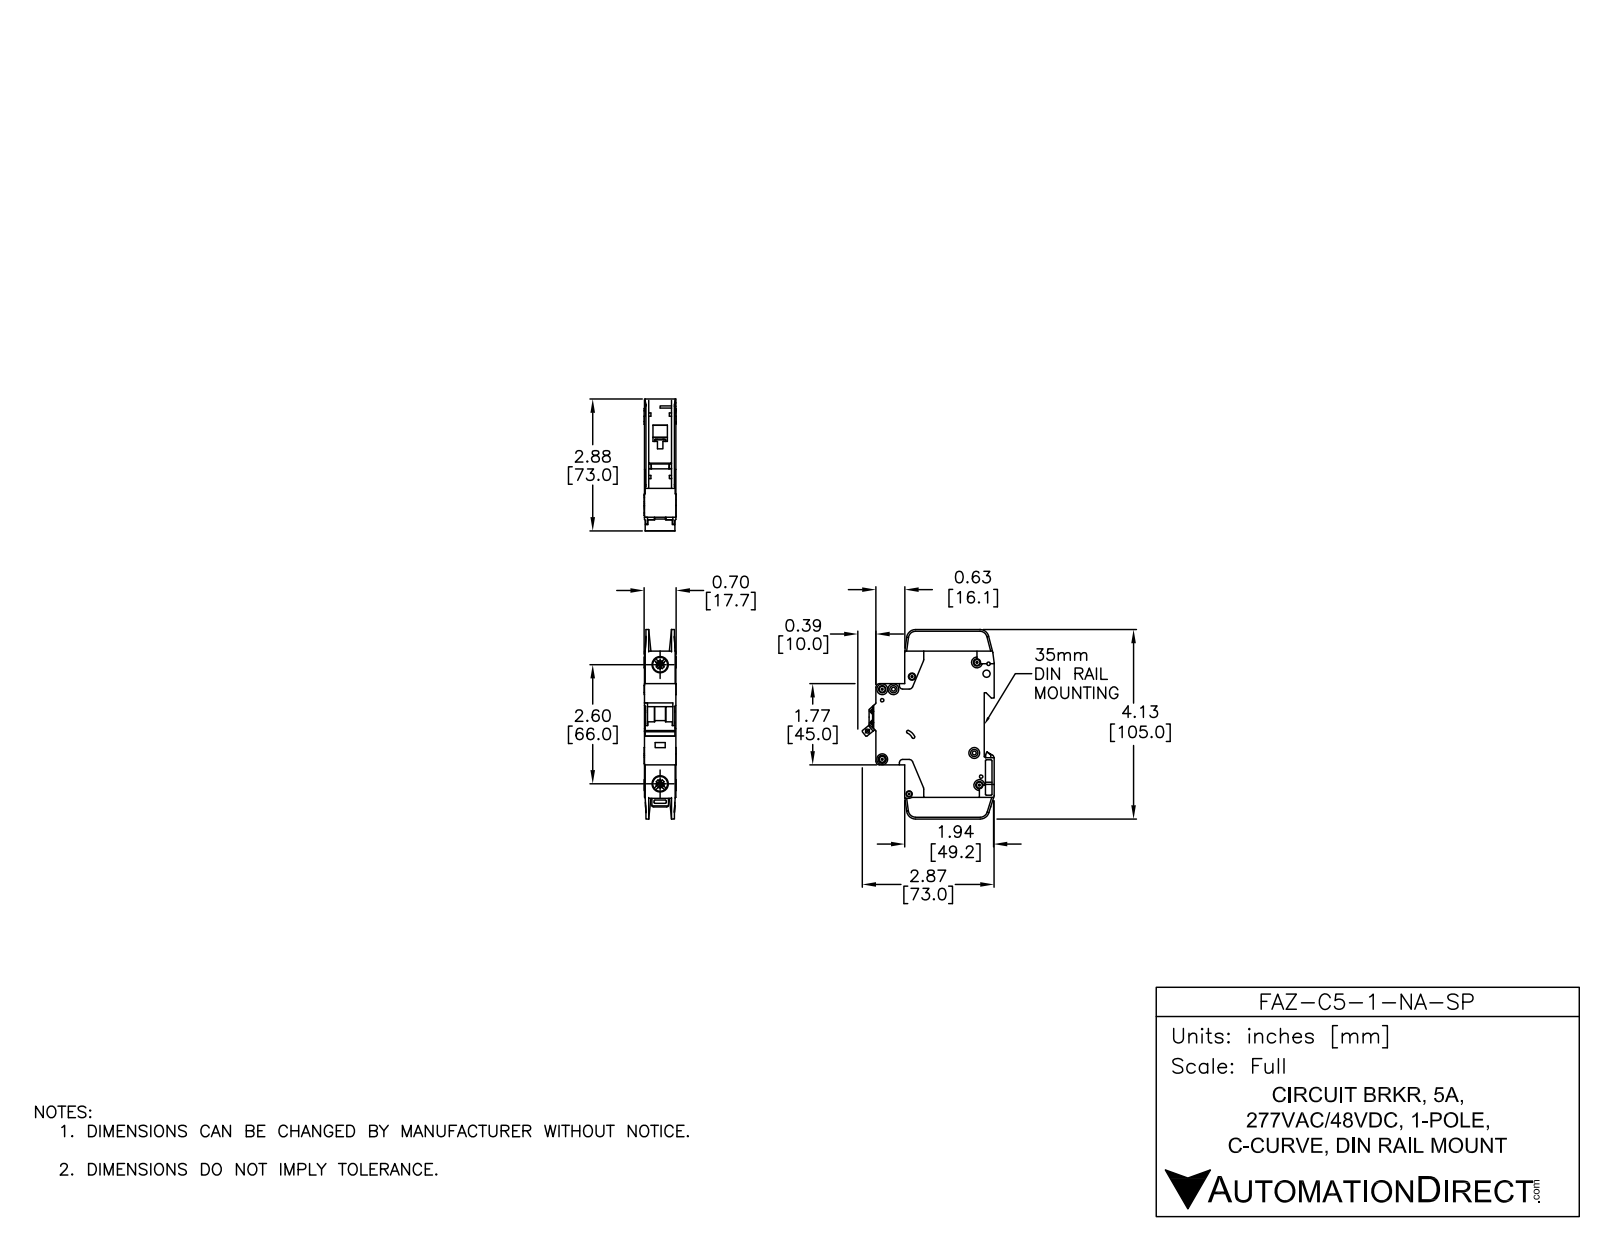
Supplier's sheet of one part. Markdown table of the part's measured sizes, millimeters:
| quantity | value |
| --- | --- |
| part name | FAZ-C50-1-NA-SP |
| STEP written by | SolidWorks 2014 (AUTOMOTIVE_DESIGN) |
| units | millimeters |
| bodies | 3 solids, 784 faces (409 planar, 263 cylindrical, 112 other) |
| overall size | 105 × 73.04 × 17.7 |
| volume | 77 695 mm³ |
| surface area | 24 740 mm² |
| round holes (diameter × count) | 3.6 × 7, 1.09 × 2, 1.5 × 2, 4 × 2, 7.15 × 2, 8.2 × 2, 1.9 × 1, 2.15 × 1, 2.2 × 1, 2.55 × 1, 3.3 × 1, 3.4 × 1 |
| round bosses / shafts (diameter × count) | 6 × 7, 2.5 × 1 |
| partial cylindrical surfaces (radius × count) | 0.25 × 29, 0.5 × 18, 1 × 10, 2 × 10, 5 × 5, 4 × 4, 1.8 × 3, 0.2 × 2 |
| main face-to-face distances | 17.5, 15.05, 0.7, 2.45, 1.75, 15.75, 13.3, 14, 12.6, 2 |
| hole center spacings | 6.2, 5.19, 6.1, 8.19, 8.56, 8.7, 11.11, 12.45 |
